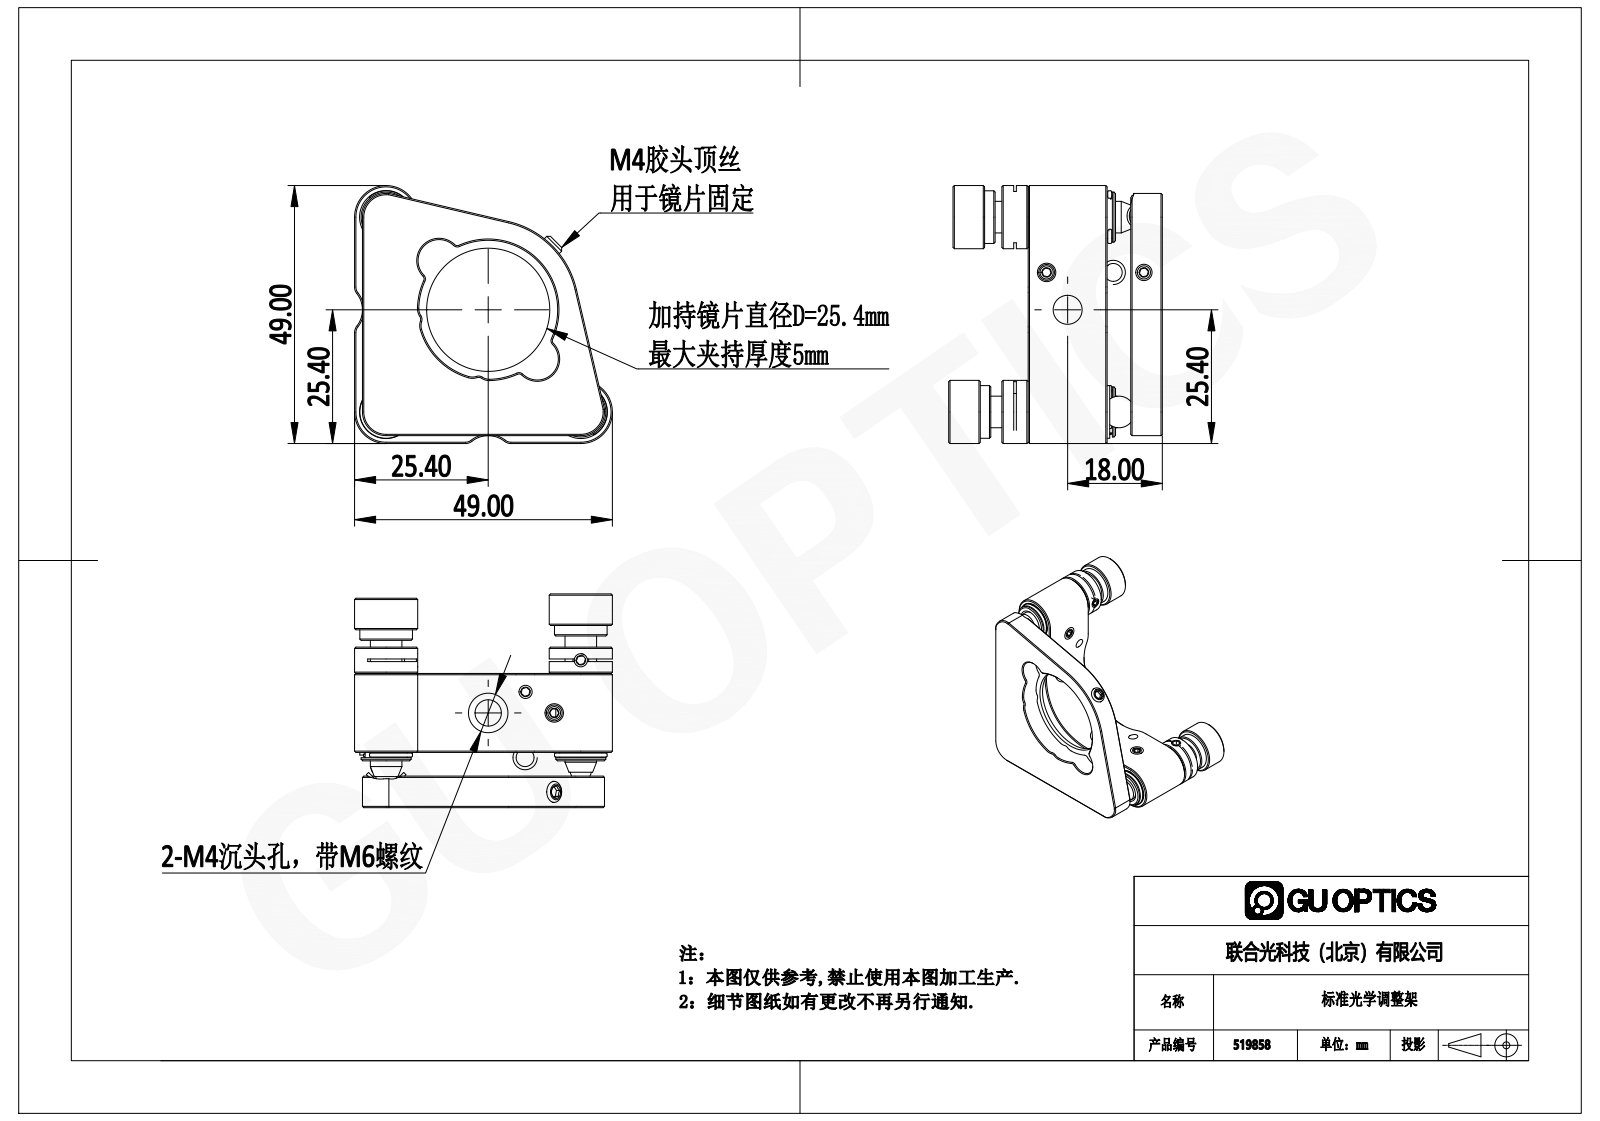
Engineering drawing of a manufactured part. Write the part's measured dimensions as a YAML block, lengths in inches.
step_written_by: "SolidWorks 2021 (AUTOMOTIVE_DESIGN)"
units: inches
bodies: {solids: 0, faces: 493, planar: 147, cylindrical: 140, other: 206}
overall_size: [1.929, 1.929, 1.598]
round_holes:
  - {diameter: 0.098, count: 3}
  - {diameter: 0.157, count: 2}
  - {diameter: 0.236, count: 2}
  - {diameter: 0.295, count: 2}
  - {diameter: 0.13, count: 1}
  - {diameter: 0.197, count: 1}
  - {diameter: 0.201, count: 1}
  - {diameter: 0.217, count: 1}
  - {diameter: 0.921, count: 1}
round_bosses_or_shafts:
  - {diameter: 0.118, count: 7}
  - {diameter: 0.394, count: 3}
  - {diameter: 0.374, count: 3}
  - {diameter: 0.157, count: 3}
  - {diameter: 0.472, count: 2}
  - {diameter: 0.315, count: 2}
  - {diameter: 0.236, count: 2}
  - {diameter: 0.35, count: 1}
partial_cylinders:
  - {radius: 0.008, count: 6}
  - {radius: 0.039, count: 5}
  - {radius: 0.079, count: 4}
  - {radius: 0.098, count: 4}
  - {radius: 0.177, count: 3}
  - {radius: 0.049, count: 2}
  - {radius: 0.157, count: 2}
  - {radius: 0.197, count: 2}
face_to_face_distances: [0.236, 0.413, 1.004, 0.177, 0.768, 0.591, 0.059, 0.197, 0.039, 0.807]
hole_center_spacings: [0.321, 0.413, 0.813, 1.031, 1.792, 0.565, 0.859, 1.476]
